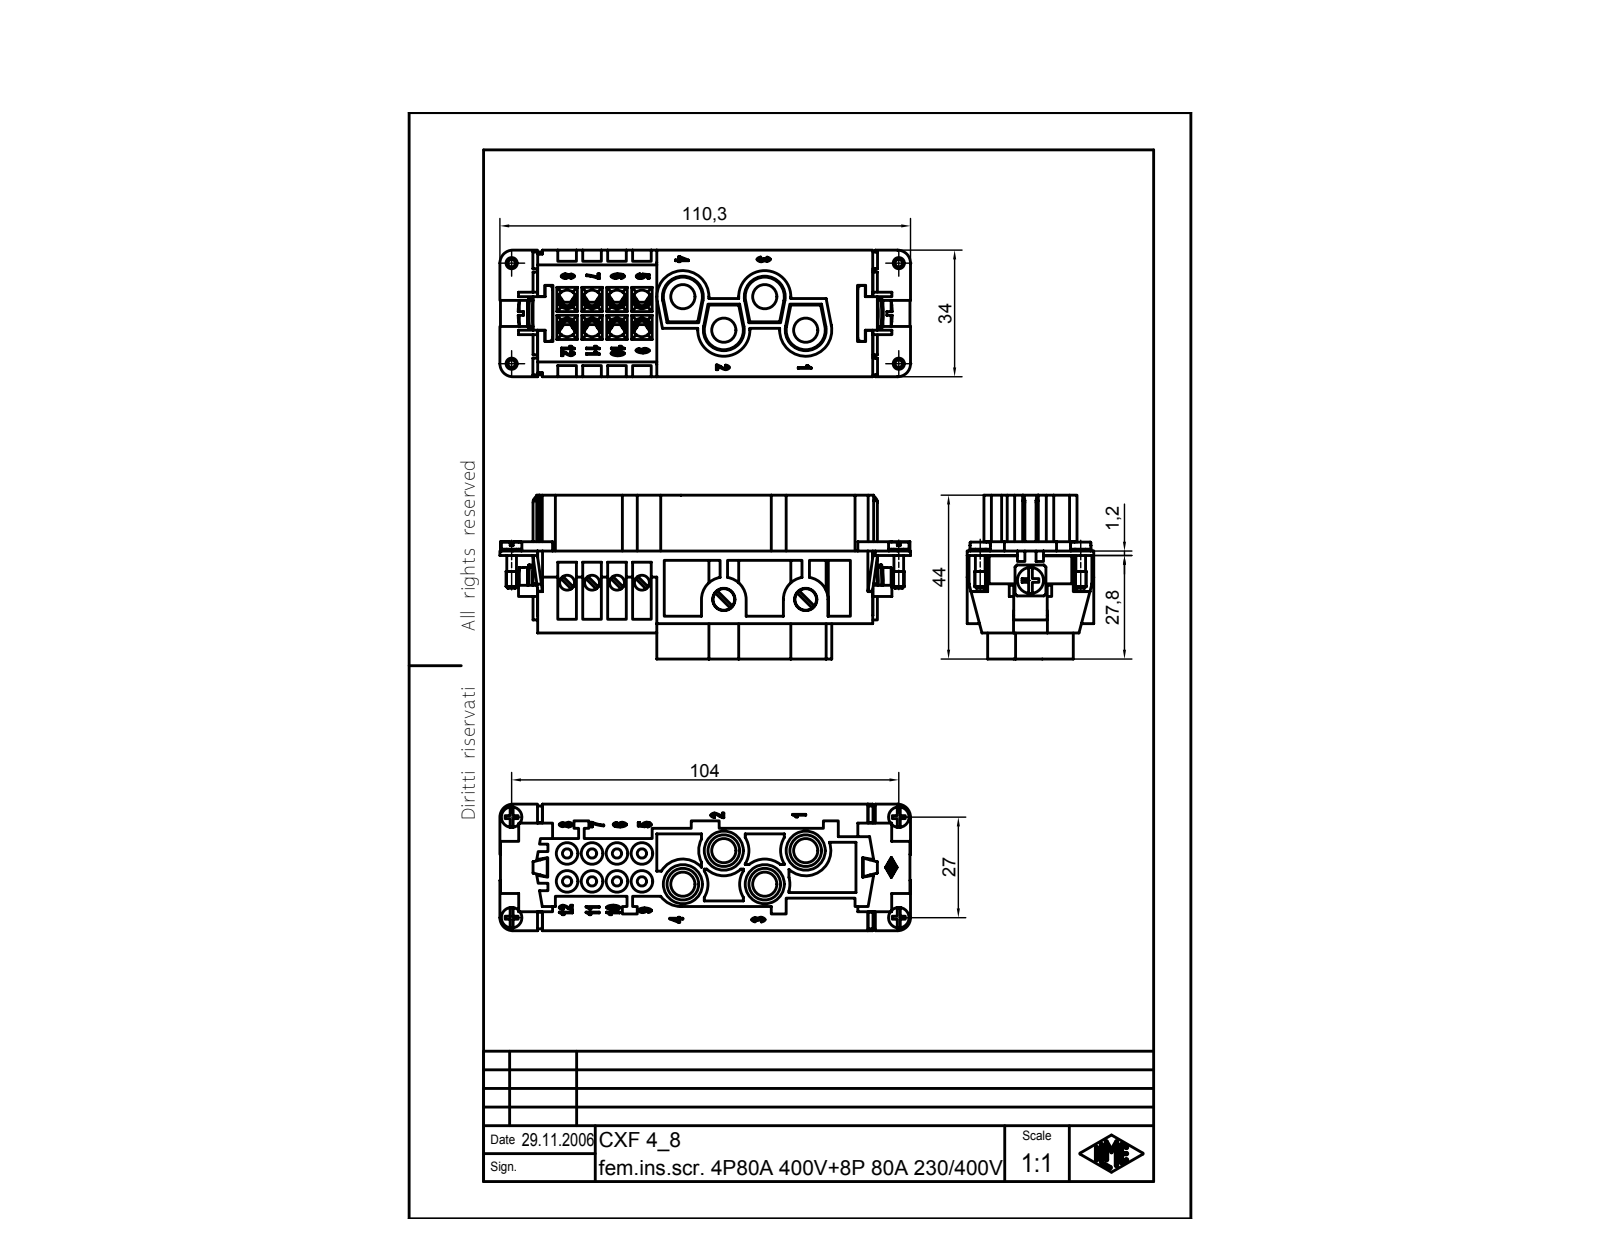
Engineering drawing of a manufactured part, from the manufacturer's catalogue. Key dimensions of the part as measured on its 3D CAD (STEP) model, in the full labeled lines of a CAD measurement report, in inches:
Part name (STEP PRODUCT): CXF 4_8
STEP written by: Autodesk Inventor 7 (AUTOMOTIVE_DESIGN)
Units: inches
Bodies: 5 solids, 1761 faces (843 planar, 263 cylindrical, 655 other)
Overall size (bounding box): 4.343 × 1.732 × 1.339
Volume: 3.906 in³ · Surface area: 68.34 in²
Round holes (diameter × count): ⌀0.197 ×8, ⌀0.118 ×4, ⌀0.157 ×4, ⌀0.236 ×4, ⌀0.256 ×4, ⌀0.128 ×1
Round bosses / shafts (diameter × count): ⌀0.228 ×4, ⌀0.217 ×2, ⌀0.209 ×2, ⌀0.118 ×2, ⌀0.102 ×2, ⌀0.276 ×1
Partial cylindrical surfaces — rounded edges, fillets, slot ends (radius × count): R0.004 ×14, R0.083 ×8, R0.217 ×5, R0.266 ×5, R0.207 ×4, R0.236 ×4, R0.276 ×4, R0.039 ×2
Main face-to-face distances: 0.768, 0.256, 0.059, 0.591, 0.098, 0.512, 0.197, 0.315, 0.453, 0.364
Hole centre spacings: 0.264, 0.528, 0.392, 0.396, 0.791, 0.289, 0.295, 0.602
